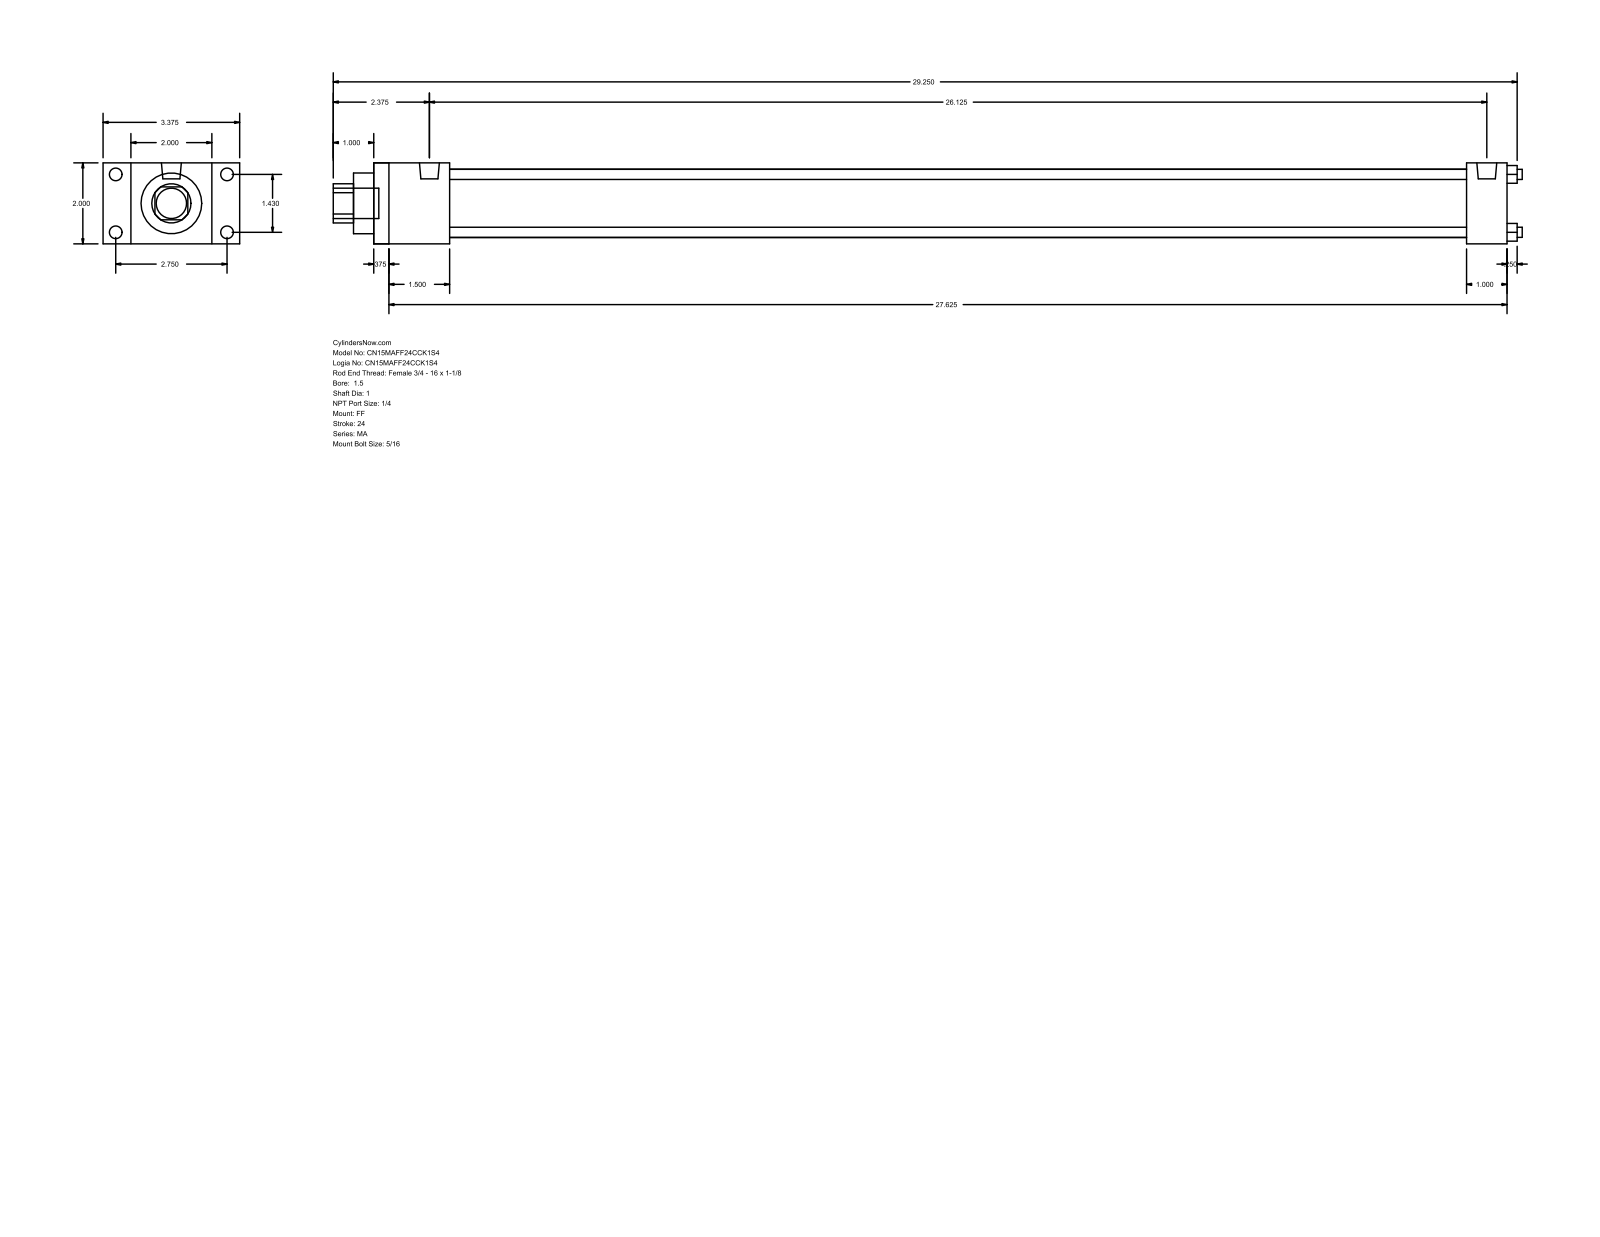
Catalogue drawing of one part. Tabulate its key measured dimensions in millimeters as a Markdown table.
| quantity | value |
| --- | --- |
| part name | MA_FF__0150_1 |
| STEP written by | GSSL Pune (CONFIG_CONTROL_DESIGN) |
| units | millimeters |
| bodies | 0 solids, 92 faces (64 planar, 28 cylindrical, 0 other) |
| overall size | 746.12 × 85.72 × 50.8 |
| round holes (diameter × count) | 6.35 × 4, 25.4 × 1, 38.1 × 1, 42.93 × 1 |
| round bosses / shafts (diameter × count) | 7.94 × 8, 12.49 × 2, 19.05 × 1 |
| partial cylindrical surfaces (radius × count) | 12.29 × 1 |
| main face-to-face distances | 50.8, 711.2, 9.52, 701.68, 25.4, 47.63, 685.8, 38.11, 676.28, 638.17 |
| hole center spacings | 25.68, 36.32, 51.36 |
